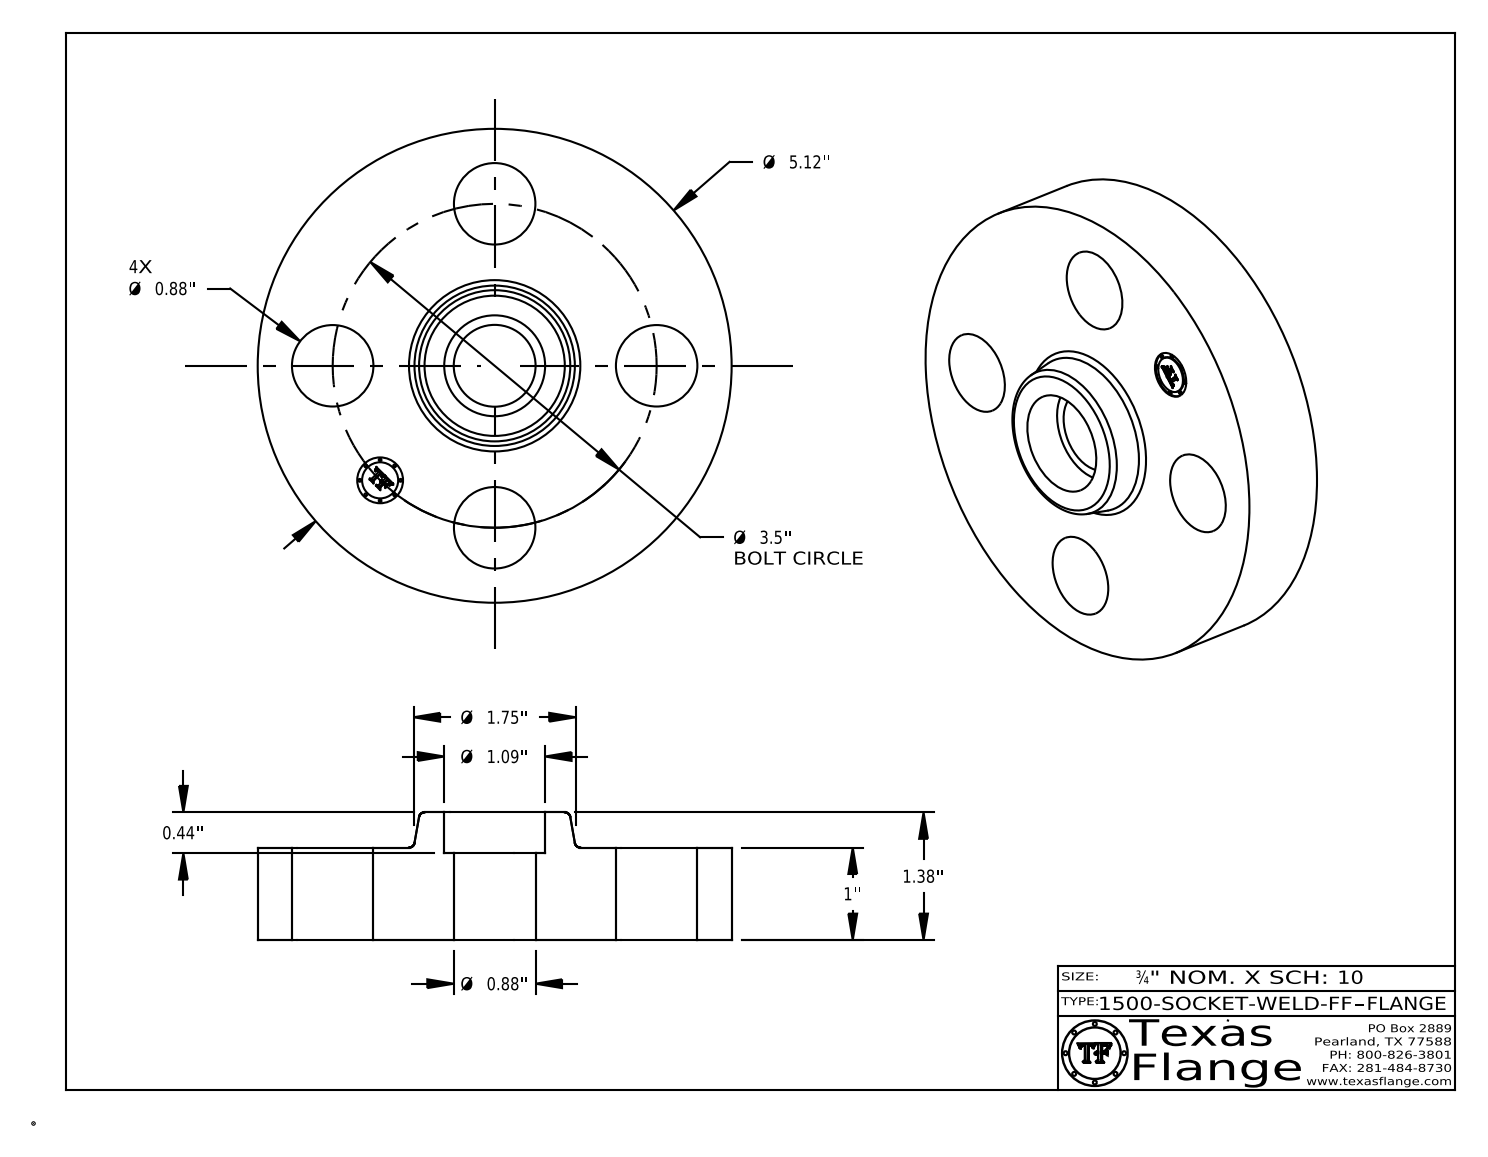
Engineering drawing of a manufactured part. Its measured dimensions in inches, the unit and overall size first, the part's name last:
Units: inches
Overall size (bounding box): 5.12 × 5.12 × 1.38
Round holes (diameter × count): ⌀0.88 ×4, ⌀0.495 ×1, ⌀0.884 ×1, ⌀1.09 ×1
Round bosses / shafts (diameter × count): ⌀0.03 ×8, ⌀5.12 ×1, ⌀0.39 ×1
Main face-to-face distances: 1, 1.38, 0.38, 0.06, 0.94, 0.44, 0.015, 0.985, 0.045, 0.395
Hole centre spacings: 1.75, 2.475, 1.339, 3.233, 3.5
Volume: 18.01 in³ · Surface area: 67.95 in²
Bodies: 1 solid, 409 faces (369 planar, 34 cylindrical, 6 other)
Part name (STEP PRODUCT): 1500-SOCKET-WELD-FF
STEP written by: CATIA V5 STEP AP214 (AUTOMOTIVE_DESIGN)
